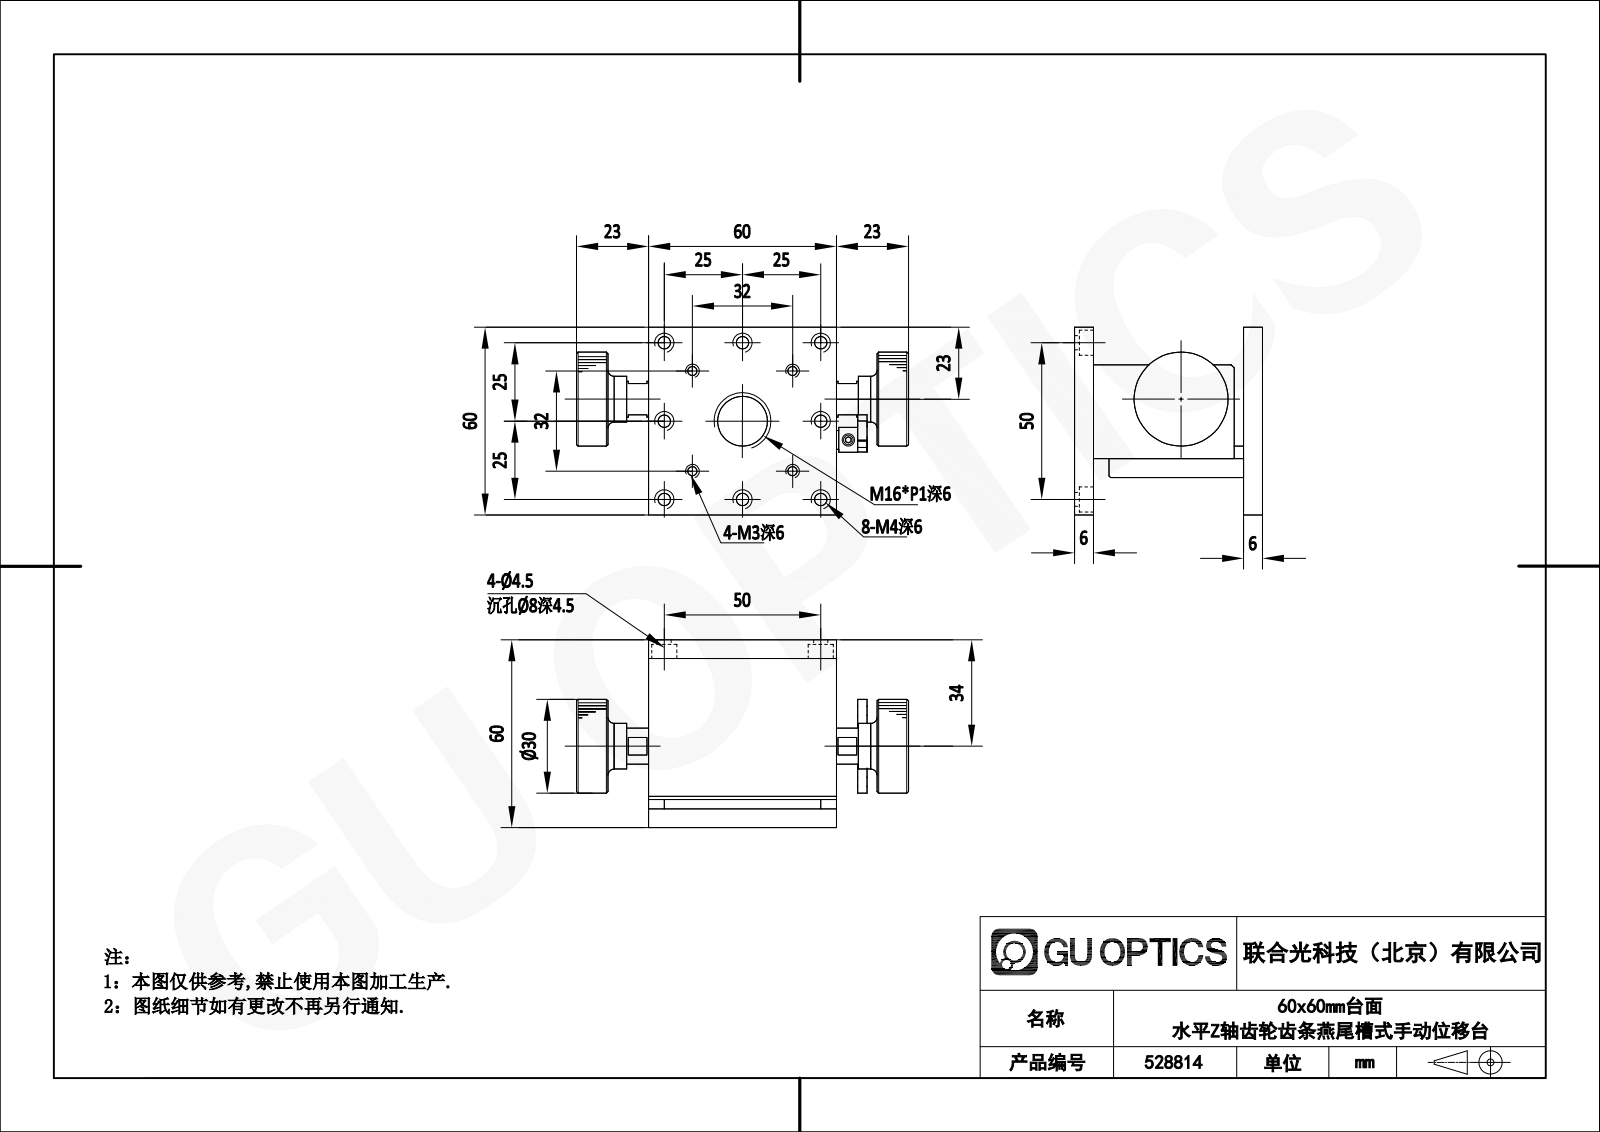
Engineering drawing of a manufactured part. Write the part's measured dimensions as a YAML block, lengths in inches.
part_name: "528814"
step_written_by: "SolidWorks 2020 (CONFIG_CONTROL_DESIGN)"
units: inches
bodies: {solids: 17, faces: 748, planar: 412, cylindrical: 175, other: 161}
overall_size: [4.528, 2.362, 2.033]
volume: 7.504
surface_area: 81.08
round_holes:
  - {diameter: 0.098, count: 21}
  - {diameter: 0.13, count: 9}
  - {diameter: 0.134, count: 6}
  - {diameter: 0.236, count: 6}
  - {diameter: 0.177, count: 4}
  - {diameter: 0.315, count: 4}
  - {diameter: 0.081, count: 2}
  - {diameter: 0.11, count: 2}
  - {diameter: 0.157, count: 1}
  - {diameter: 0.453, count: 1}
  - {diameter: 0.63, count: 1}
round_bosses_or_shafts:
  - {diameter: 0.217, count: 6}
  - {diameter: 0.118, count: 6}
  - {diameter: 0.787, count: 1}
  - {diameter: 0.413, count: 1}
  - {diameter: 0.362, count: 1}
  - {diameter: 0.354, count: 1}
  - {diameter: 0.276, count: 1}
  - {diameter: 0.27, count: 1}
partial_cylinders:
  - {radius: 0.039, count: 8}
  - {radius: 0.059, count: 2}
  - {radius: 0.299, count: 2}
  - {radius: 0.394, count: 2}
  - {radius: 0.197, count: 1}
  - {radius: 0.346, count: 1}
  - {radius: 0.65, count: 1}
face_to_face_distances: [0.236, 1.732, 1.496, 1.969, 1.319, 2.362, 0.02, 0.374, 0.945, 0.217]
hole_center_spacings: [0.984, 0.723, 1.392, 1.653, 1.733, 2.201, 0.787, 1.969]
